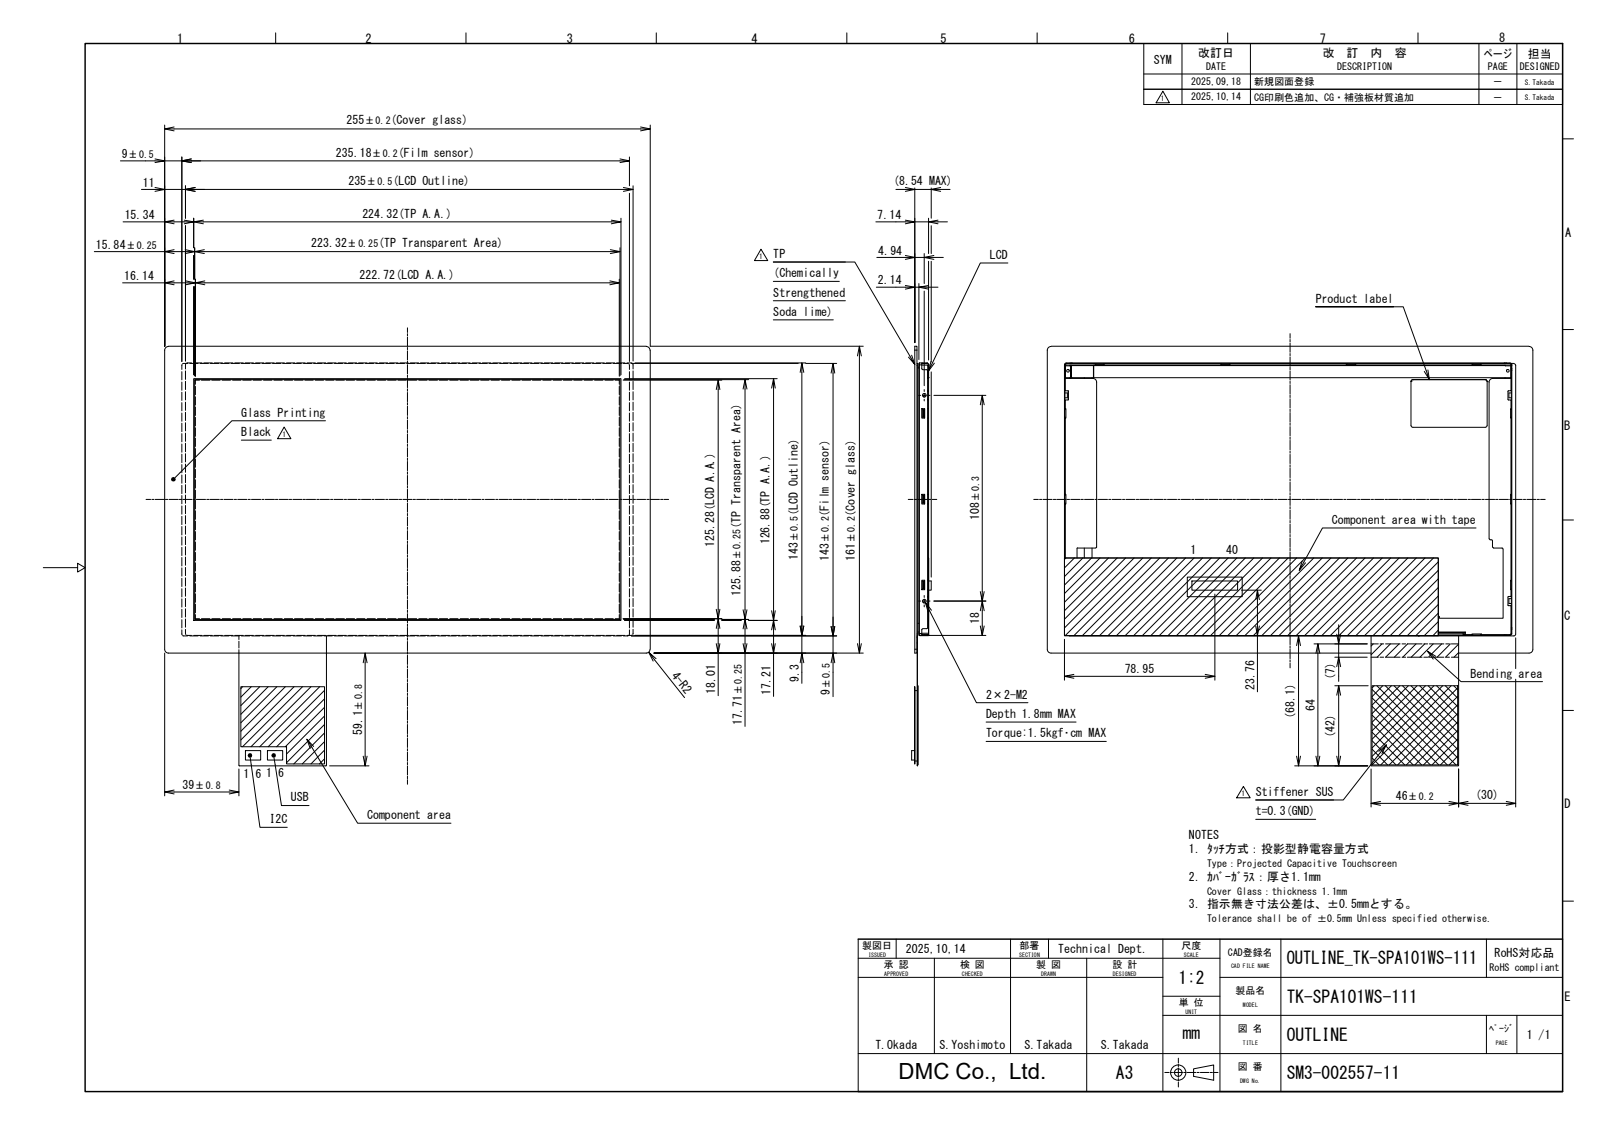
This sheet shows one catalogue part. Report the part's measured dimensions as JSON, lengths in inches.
{"part_name": "HP_TK-SPA101WS-111", "step_written_by": "Autodesk Inventor 2024 (AUTOMOTIVE_DESIGN)", "units": "inches", "bodies": {"solids": 2, "faces": 860, "planar": 727, "cylindrical": 123, "other": 10}, "overall_size": [10.039, 8.665, 0.403], "volume_in3": 10.14, "surface_area_in2": 417.9, "round_holes": [[0.051, 2], [0.079, 2], [0.039, 1]], "round_bosses_or_shafts": [[0.102, 2], [0.031, 1]], "partial_cylinders_radius": [[0.012, 30], [0.02, 14], [0.039, 12], [0.004, 8], [0.01, 7], [0.079, 6], [0.024, 4], [0.028, 4]], "face_to_face_distances": [0.059, 0.05, 0.042, 0.101, 0.151, 0.092, 0.037, 0.284, 0.186, 0.131], "hole_center_spacings": [4.252, 9.098]}
